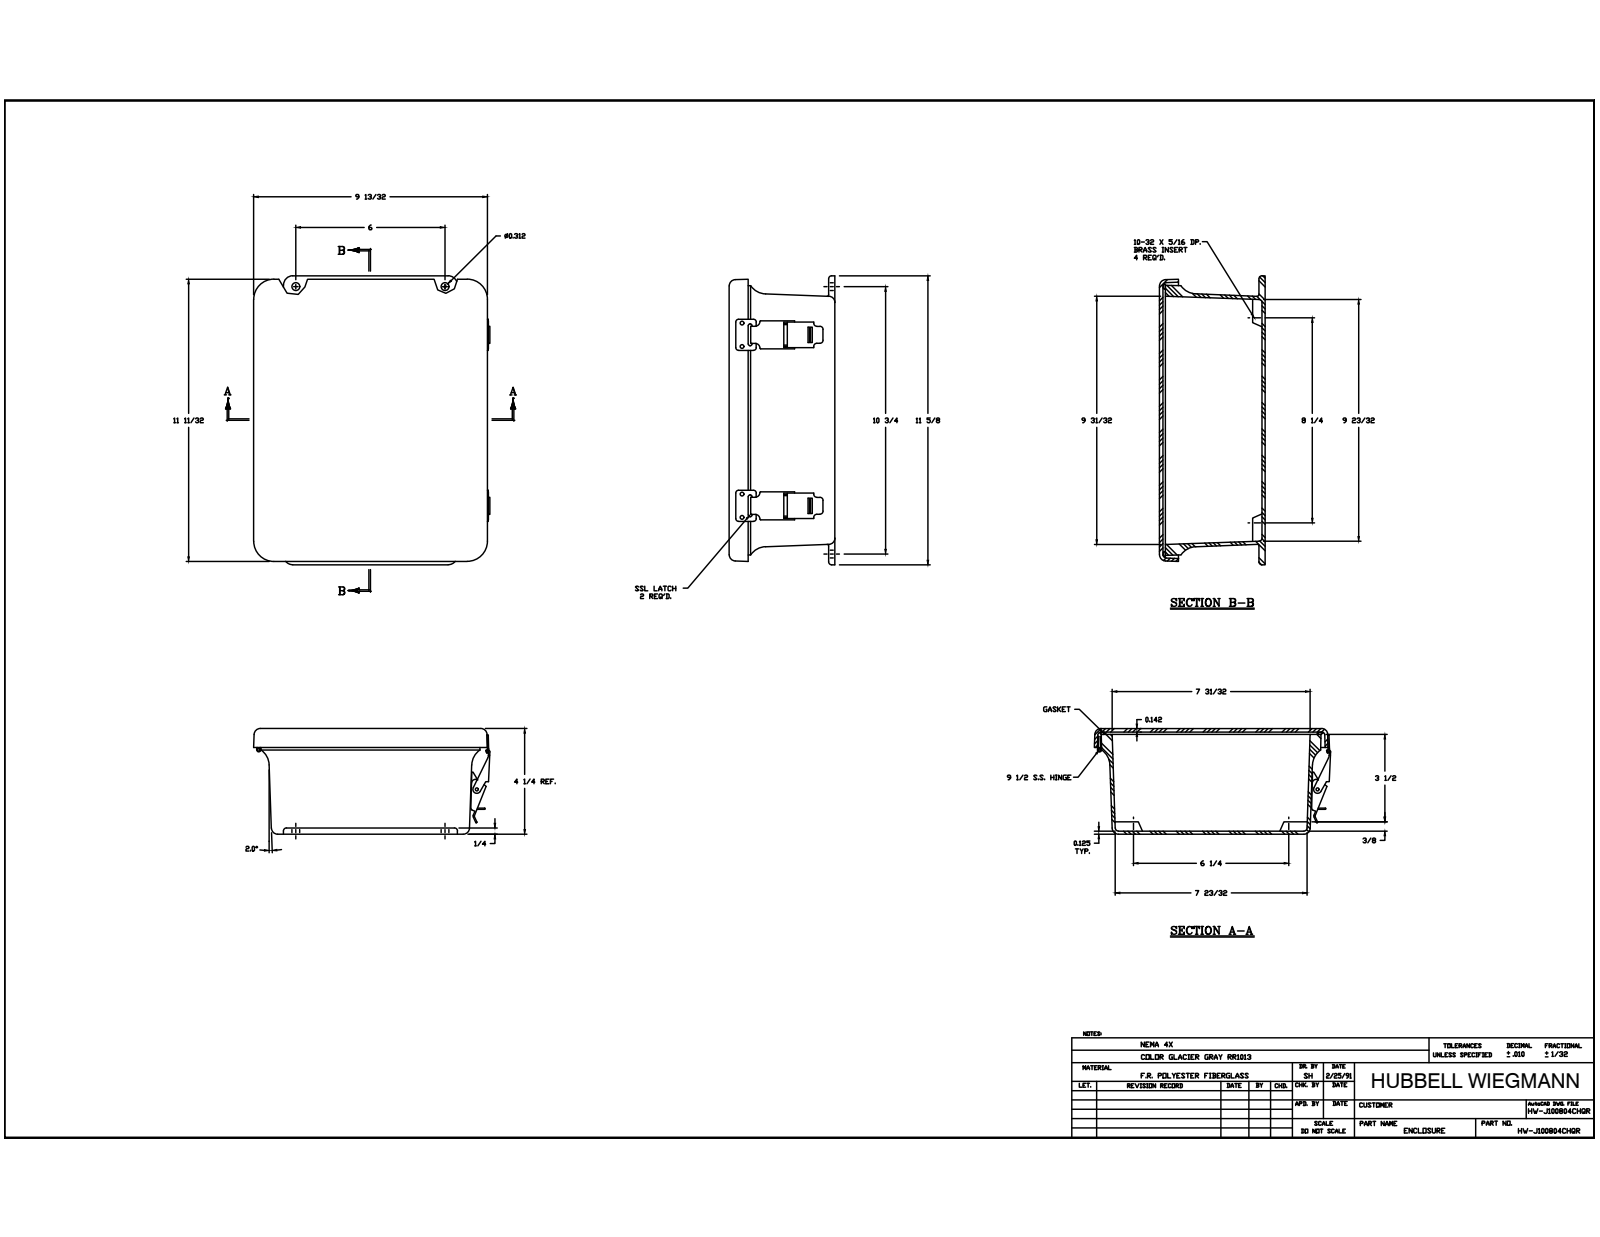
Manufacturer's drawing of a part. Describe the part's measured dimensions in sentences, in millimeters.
The part is named "J1008HL_1; RMINS45821P_29; RMINS45821P_30; RMINS45821P_31 (+8 more)". Its 3-D file was written by "Autodesk Inventor 2014 (AUTOMOTIVE_DESIGN)". It is 38 solids with 939 faces: 399 planar, 393 cylindrical and 147 other. Overall it measures 295.27 by 242.13 by 107.56 millimeters. Its volume is 1 004 000 cubic millimeters and its surface area 540 476 square millimeters. Round holes: 20 of diameter 3.56, 8 of diameter 2.64, 8 of diameter 3.33, 5 of diameter 3.86, 4 of diameter 3.3, 4 of diameter 3.96, 4 of diameter 5.54, 2 of diameter 3.43, 2 of diameter 9.52, 1 of diameter 2.16, 1 of diameter 2.16. Round bosses or shafts: 16 of diameter 3.17, 8 of diameter 6.35, 4 of diameter 6.86, 1 of diameter 7.62, 1 of diameter 4.31, 1 of diameter 3.94, 1 of diameter 3.05. Partial cylindrical surfaces (rounded edges, fillets, slot ends): 20 of radius 0.38, 20 of radius 0.79, 20 of radius 3.17, 16 of radius 1.14, 12 of radius 0.76, 9 of radius 0.57, 8 of radius 6.35, 6 of radius 1.52. The main face-to-face distances are 3.61, 103.95, 107.56, 3.17, 100.78, 104.39, 3.05, 98.81, 101.98, 1.97. The hole center spacings are 177.8, 19.05, 178.82, 23.81, 152.4, 76.2, 6.35, 37.29.
